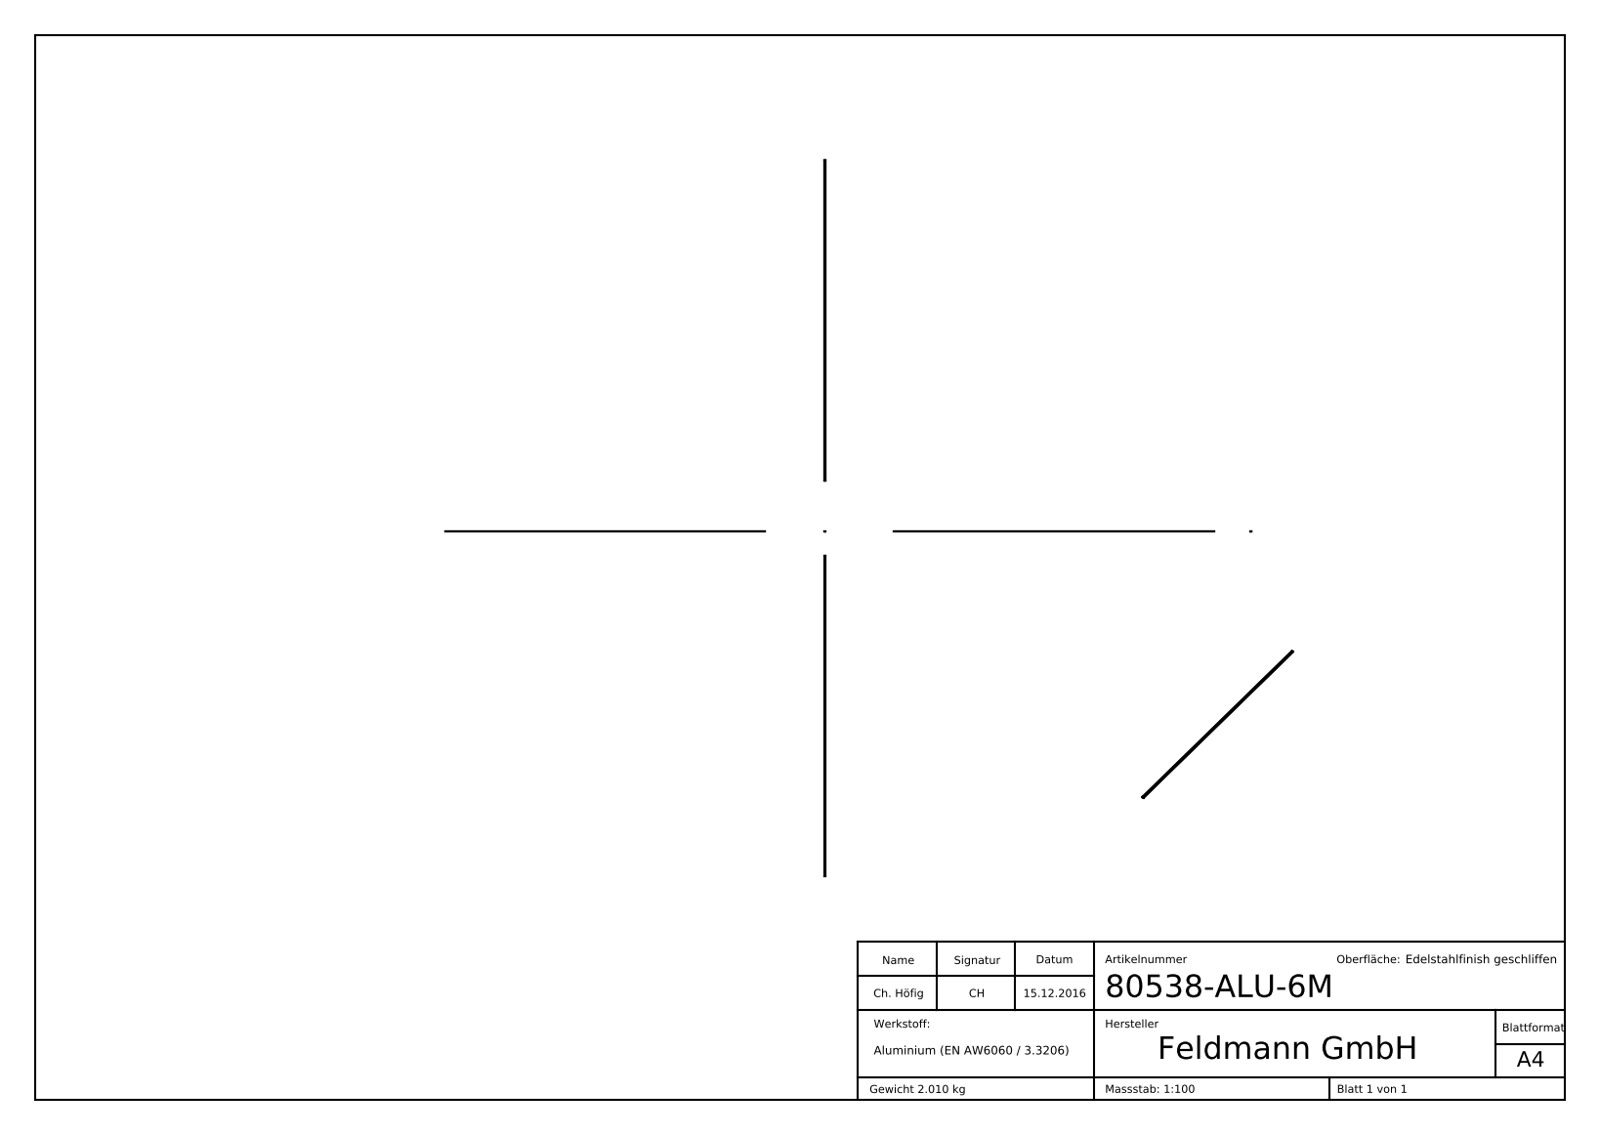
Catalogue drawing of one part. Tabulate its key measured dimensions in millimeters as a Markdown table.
| quantity | value |
| --- | --- |
| part name | 80538-ALU-6M |
| STEP written by | SolidWorks 2015 (CONFIG_CONTROL_DESIGN) |
| units | millimeters |
| bodies | 1 solid, 285 faces (150 planar, 6 cylindrical, 129 other) |
| overall size | 6000 × 24 × 12 |
| volume | 744 411 mm³ |
| surface area | 524 808 mm² |
| partial cylindrical surfaces (radius × count) | 0.5 × 4, 2 × 2 |
| main face-to-face distances | 3, 21, 24, 18, 9, 12, 6000, 2.9, 18.1, 21.1 |
